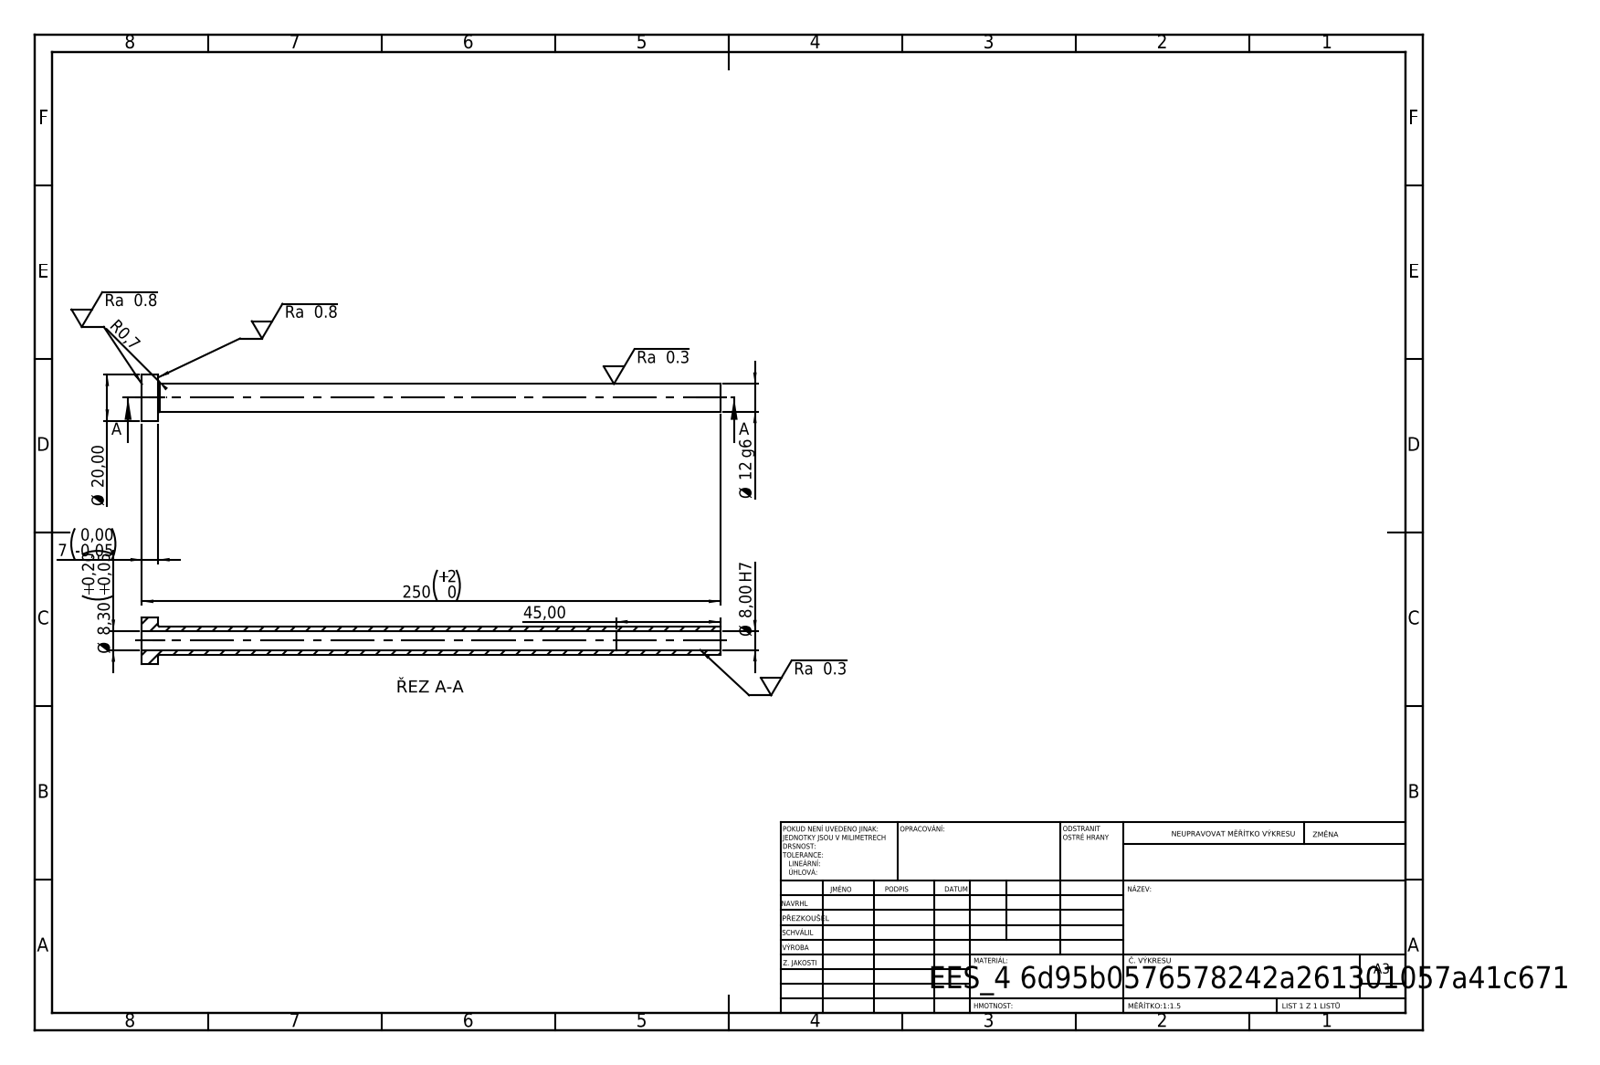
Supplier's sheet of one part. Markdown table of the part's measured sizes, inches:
| quantity | value |
| --- | --- |
| STEP written by | SolidWorks 2019 (CONFIG_CONTROL_DESIGN) |
| units | inches |
| bodies | 1 solid, 14 faces (4 planar, 8 cylindrical, 2 other) |
| overall size | 9.843 × 0.787 × 0.787 |
| volume | 0.997 in³ |
| surface area | 25.72 in² |
| round holes (diameter × count) | 0.315 × 1, 0.327 × 1 |
| round bosses / shafts (diameter × count) | 0.787 × 1, 0.472 × 1 |
| main face-to-face distances | 0.276, 9.843, 9.567, 8.071, 7.795, 1.772 |
